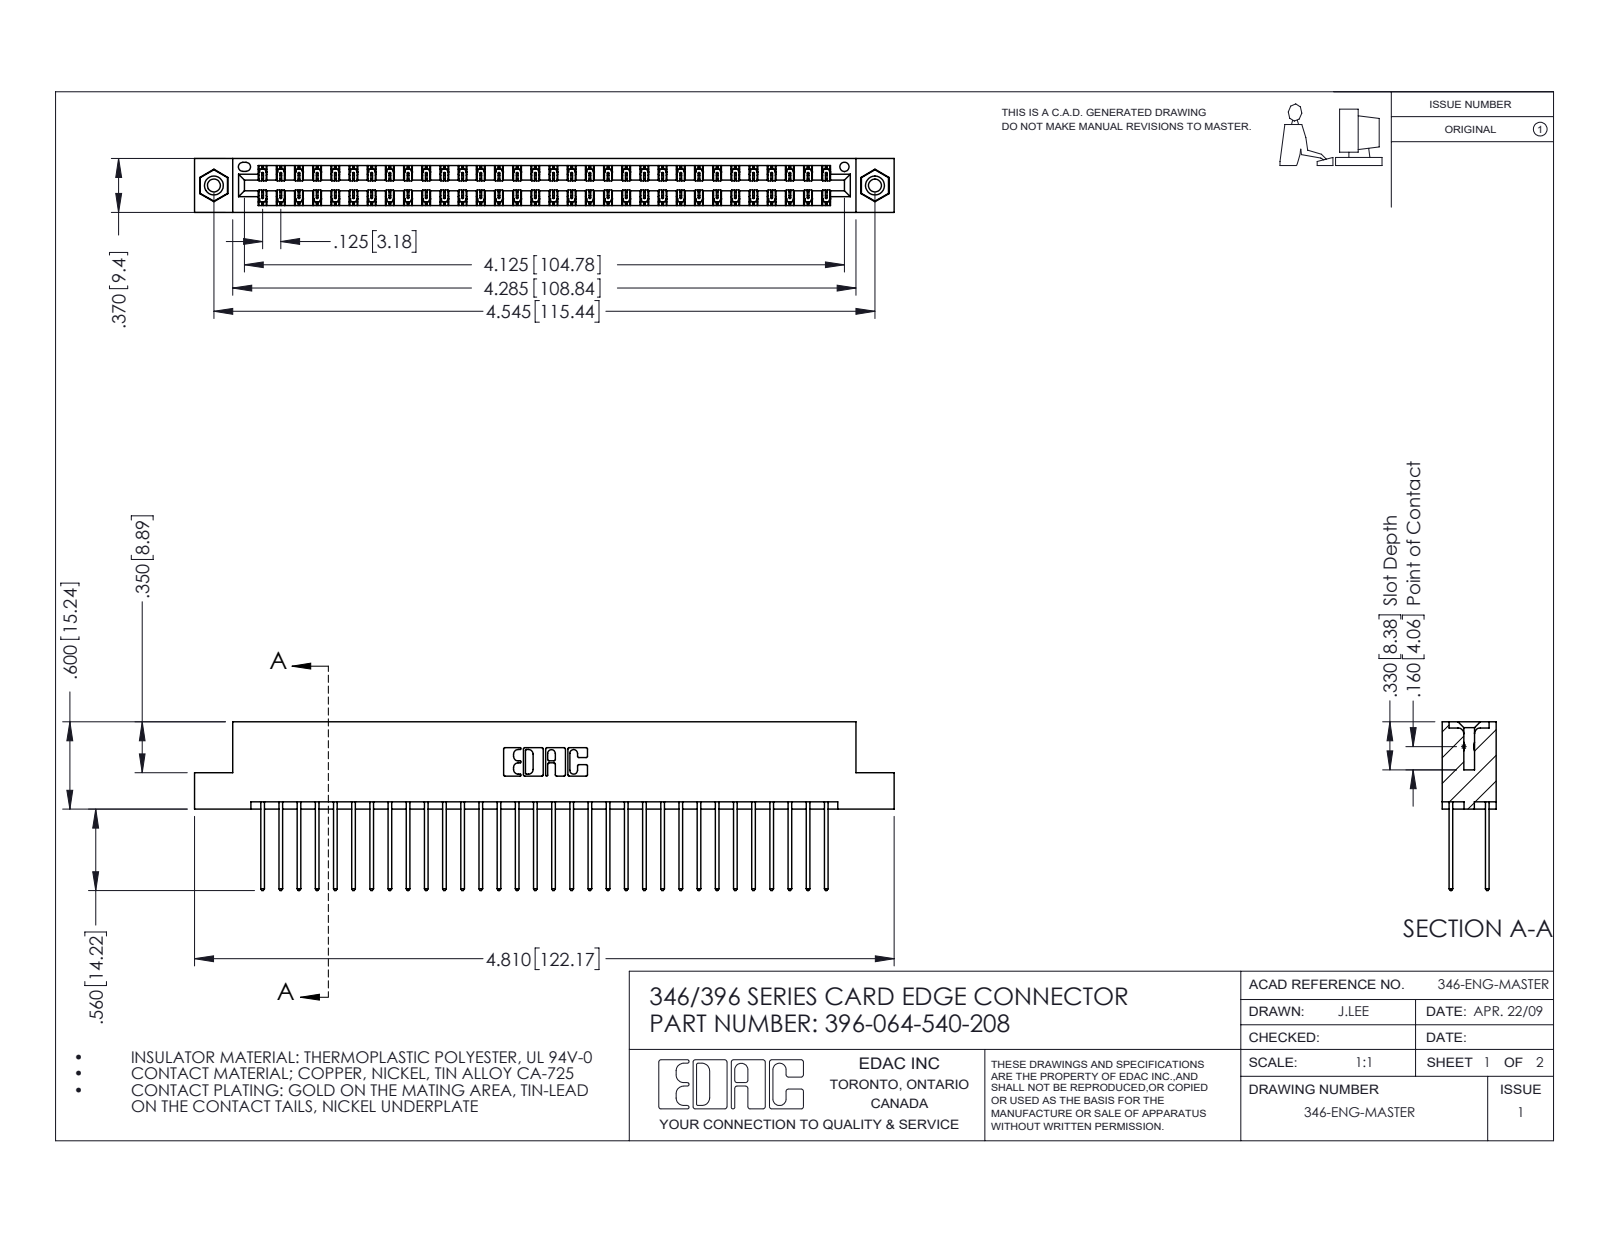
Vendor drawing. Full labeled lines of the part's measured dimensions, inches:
Part name (STEP PRODUCT): 345-292-001_345-293-140; 396-064-540-208; 346 Part_Flush Mounting Lugs - 0.156 Dia-TI; 345-250-001_345-250-003-102
STEP written by: SolidWorks 2016 (CONFIG_CONTROL_DESIGN)
Units: inches
Bodies: 67 solids, 3510 faces (2348 planar, 1146 cylindrical, 16 other)
Overall size (bounding box): 4.81 × 1.16 × 0.37
Volume: 0.737 in³ · Surface area: 27.29 in²
Round holes (diameter × count): ⌀0.089 ×2, ⌀0.125 ×2, ⌀0.156 ×2, ⌀0.064 ×1
Round bosses / shafts (diameter × count): ⌀0.155 ×2
Partial cylindrical surfaces — rounded edges, fillets, slot ends (radius × count): R0.006 ×96, R0.01 ×64, R0.01 ×22, R0.007 ×6, R0.031 ×6, R0.026 ×3, R0.014 ×2, R0.022 ×2
Main face-to-face distances: 0.048, 0.322, 0.25, 0.072, 0.298, 0.025, 0.37, 0.275, 0.148, 0.222
Hole centre spacings: 0.246, 4.337, 4.545
